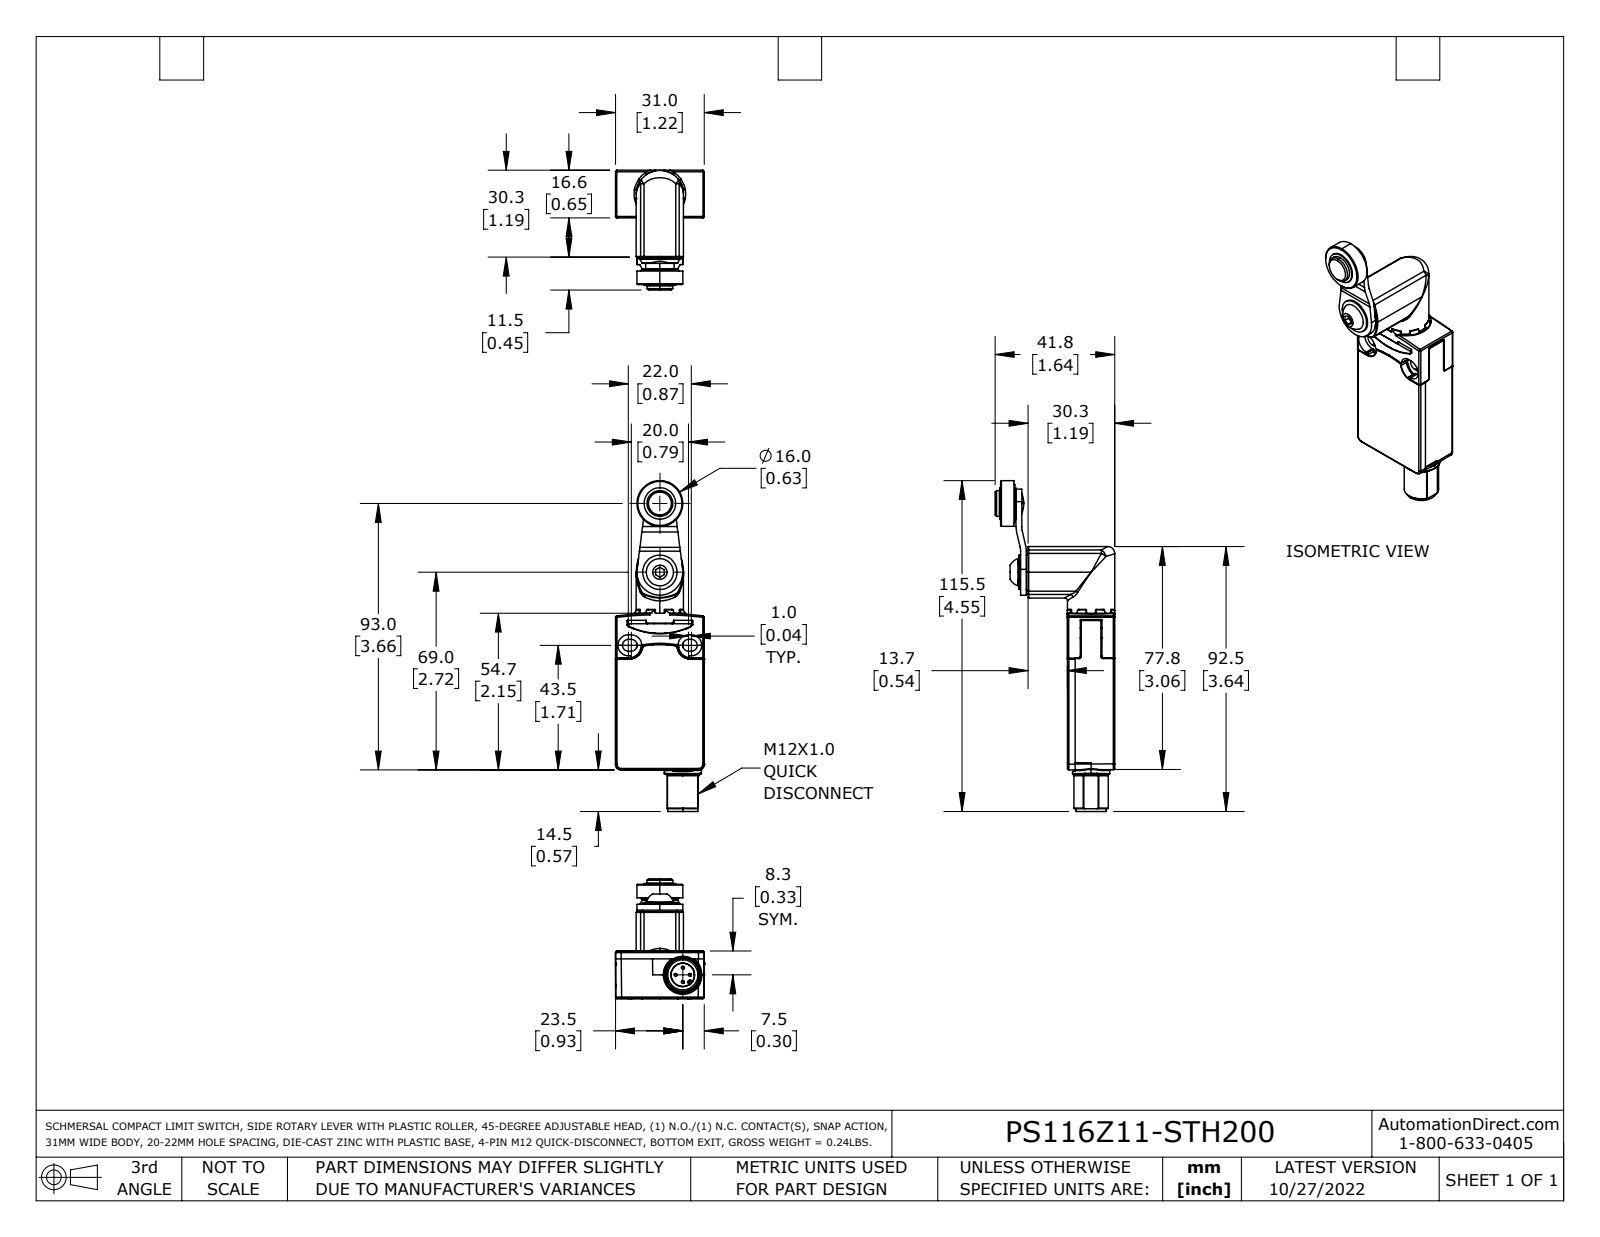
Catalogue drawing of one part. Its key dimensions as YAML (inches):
part_name: "PS116Z11-STH200_Default"
step_written_by: "SolidWorks 2021 (CONFIG_CONTROL_DESIGN)"
units: inches
bodies: {solids: 1, faces: 955, planar: 288, cylindrical: 416, other: 251}
overall_size: [4.548, 1.646, 1.22]
volume: 2.308
surface_area: 25.16
round_holes:
  - {diameter: 0.079, count: 1}
  - {diameter: 0.327, count: 1}
  - {diameter: 0.48, count: 1}
  - {diameter: 0.571, count: 1}
  - {diameter: 0.583, count: 1}
round_bosses_or_shafts:
  - {diameter: 0.039, count: 4}
  - {diameter: 0.512, count: 2}
  - {diameter: 0.65, count: 1}
  - {diameter: 0.63, count: 1}
  - {diameter: 0.567, count: 1}
  - {diameter: 0.524, count: 1}
  - {diameter: 0.475, count: 1}
  - {diameter: 0.472, count: 1}
partial_cylinders:
  - {radius: 0.008, count: 110}
  - {radius: 0.004, count: 67}
  - {radius: 0.02, count: 34}
  - {radius: 0.014, count: 10}
  - {radius: 0.039, count: 8}
  - {radius: 0.079, count: 5}
  - {radius: 0.081, count: 4}
  - {radius: 0.098, count: 4}
face_to_face_distances: [0.65, 0.652, 0.079, 1.22, 0.063, 0.118, 0.654, 0.016, 0.453, 0.291]
hole_center_spacings: [0.315]
